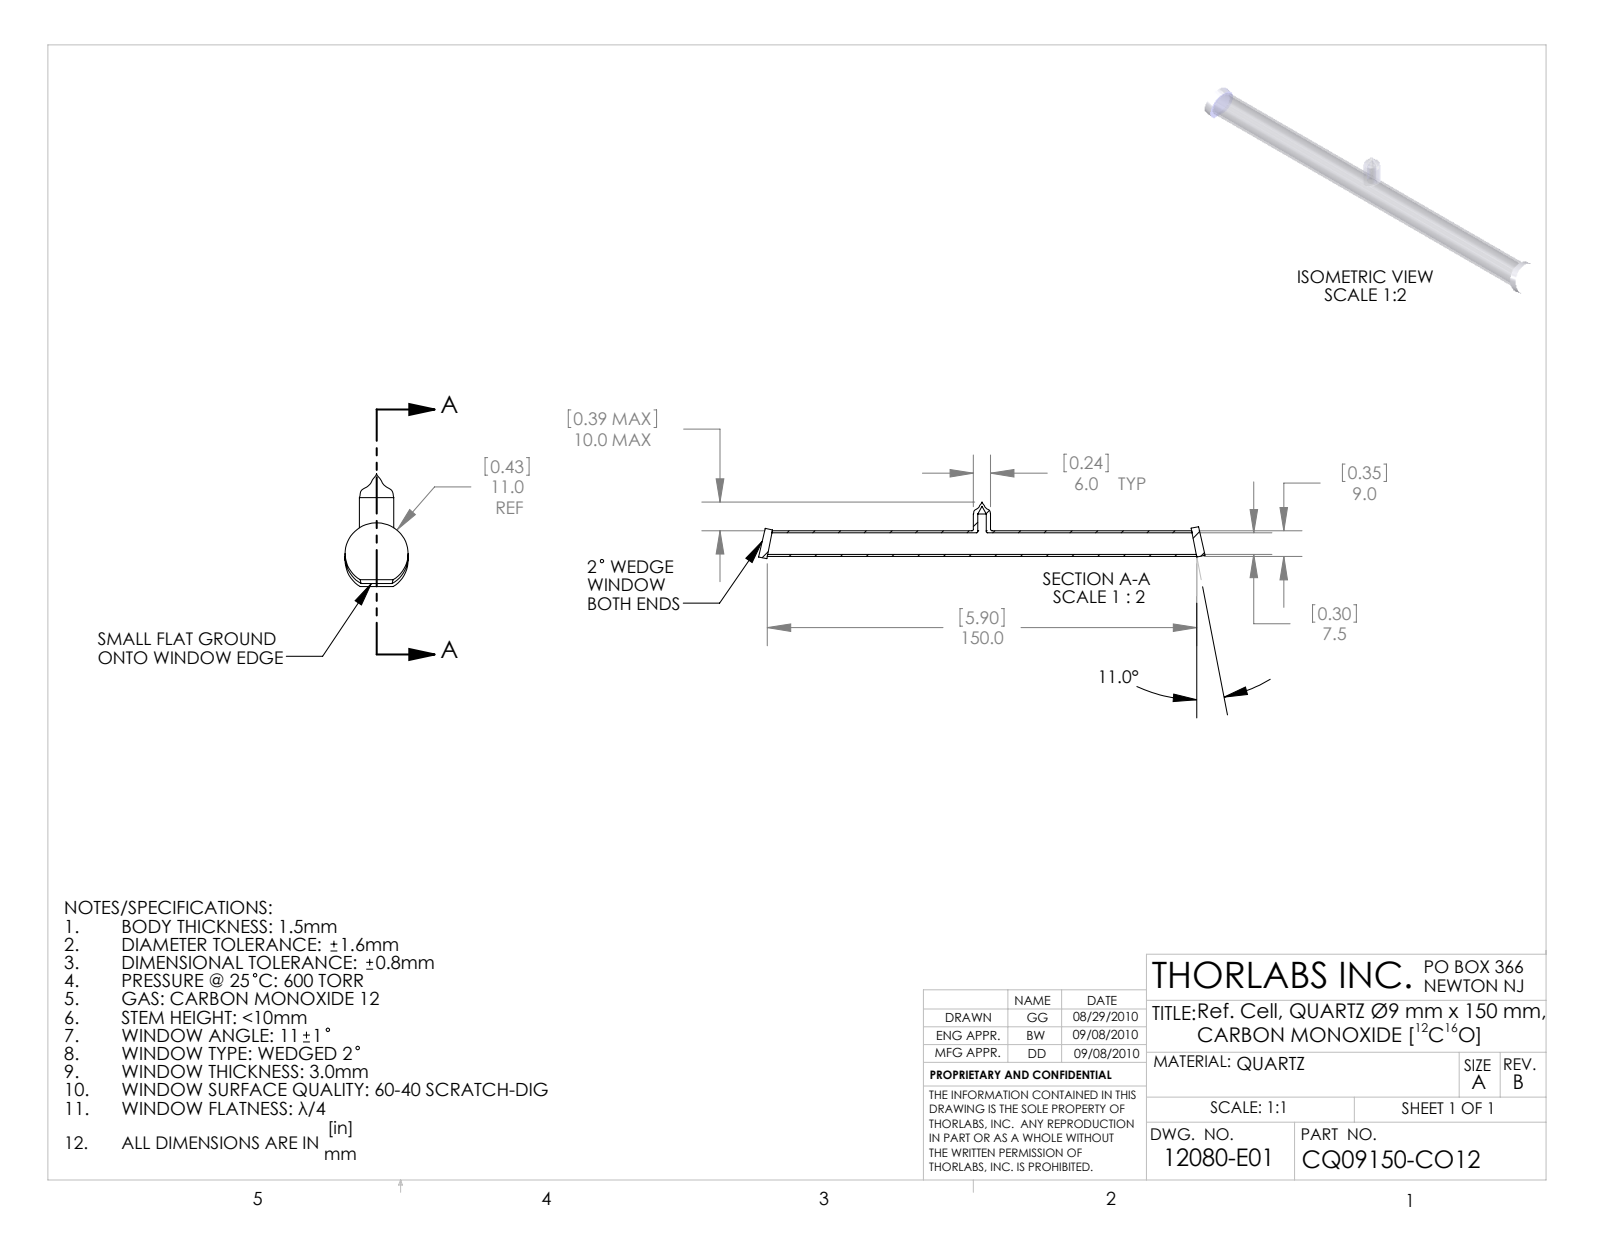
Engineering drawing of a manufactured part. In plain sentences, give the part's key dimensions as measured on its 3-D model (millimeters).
The part is named "12080-E0W". Its 3-D file was written by "SolidWorks 2009 (AUTOMOTIVE_DESIGN)". It is 3 solids with 33 faces: 8 planar, 17 cylindrical and 8 other. Overall it measures 155.95 by 19.74 by 11 millimeters. Its volume is 3 563 cubic millimeters and its surface area 8 494 square millimeters. Round holes: 1 of diameter 2.91, 1 of diameter 3, 1 of diameter 7.5. Round bosses or shafts: 2 of diameter 11, 1 of diameter 9, 1 of diameter 6.
